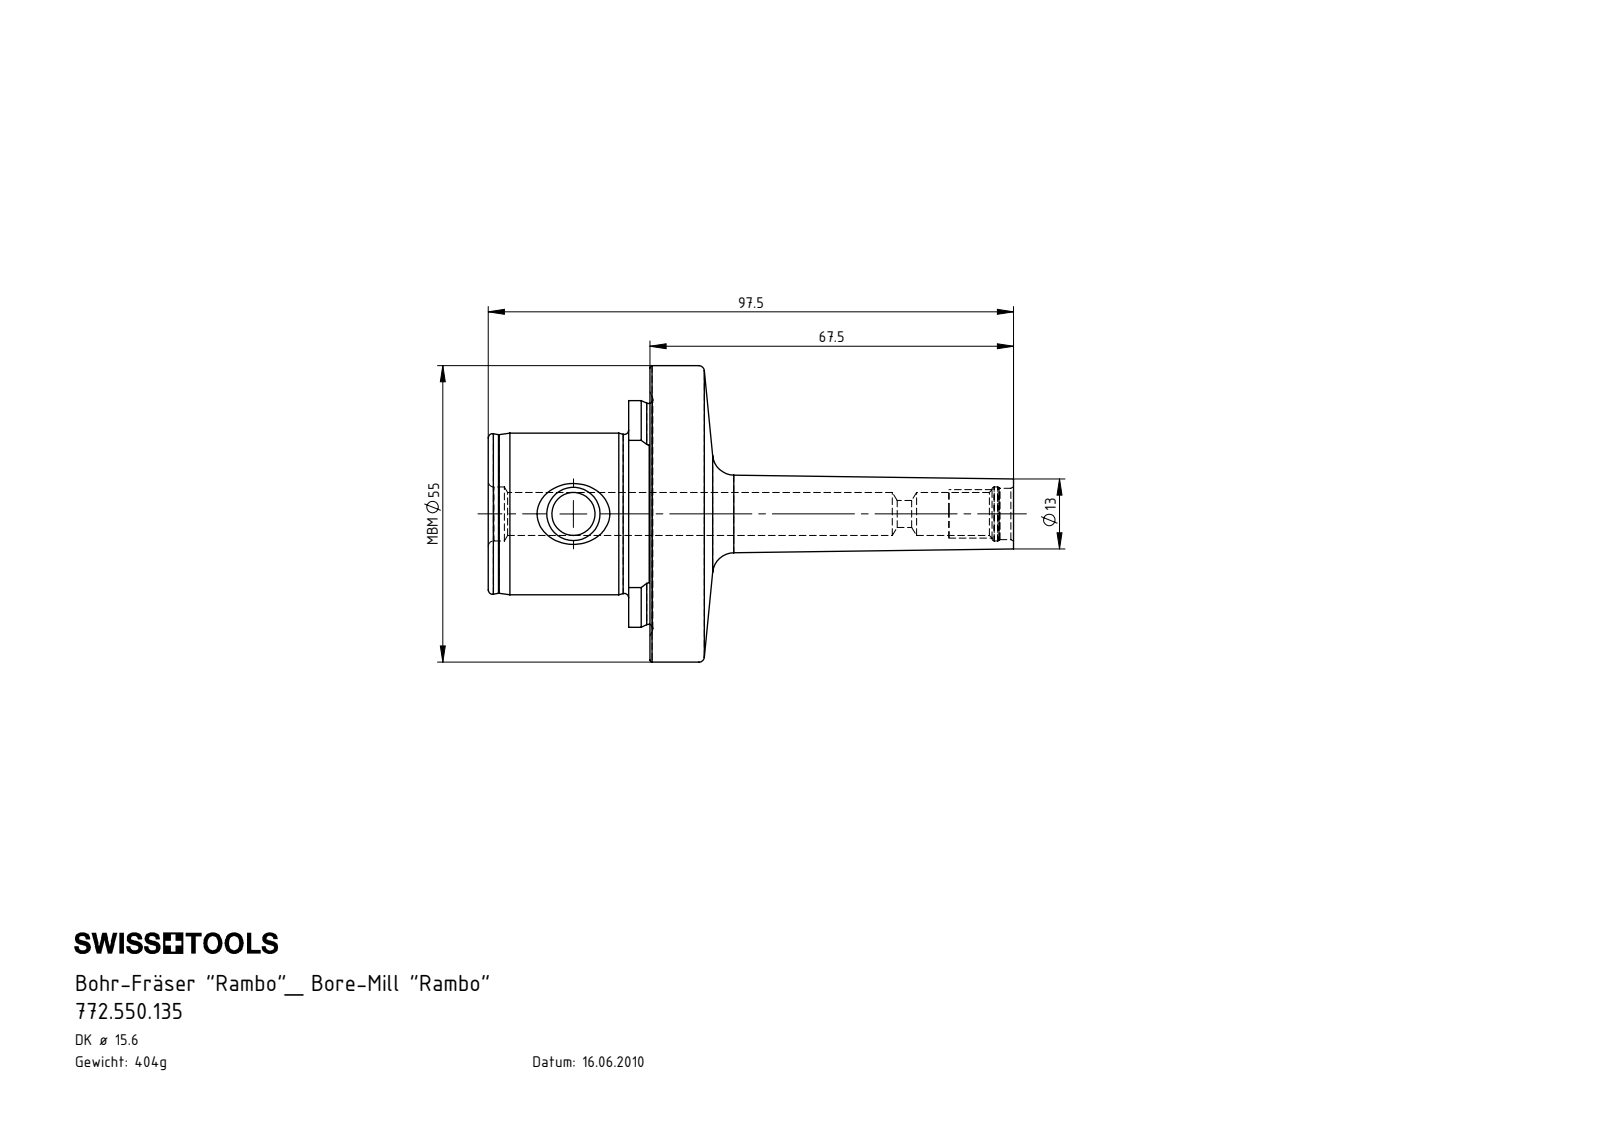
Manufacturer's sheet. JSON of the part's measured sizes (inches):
{"part_name": "772.550.135", "step_written_by": "SolidWorks 2017 (CONFIG_CONTROL_DESIGN)", "units": "inches", "bodies": {"solids": 1, "faces": 90, "planar": 9, "cylindrical": 22, "other": 59}, "overall_size": [3.839, 2.165, 2.165], "volume_in3": 3.142, "surface_area_in2": 22.05, "round_holes": [[0.315, 2], [0.197, 1], [0.374, 1], [0.394, 1]], "round_bosses_or_shafts": [[2.165, 1], [1.181, 1]], "partial_cylinders_radius": [[0.828, 1]], "face_to_face_distances": [1.181, 1.026, 0.156, 1.175, 0.15, 1.26, 3.839, 2.813, 2.663, 2.657]}
